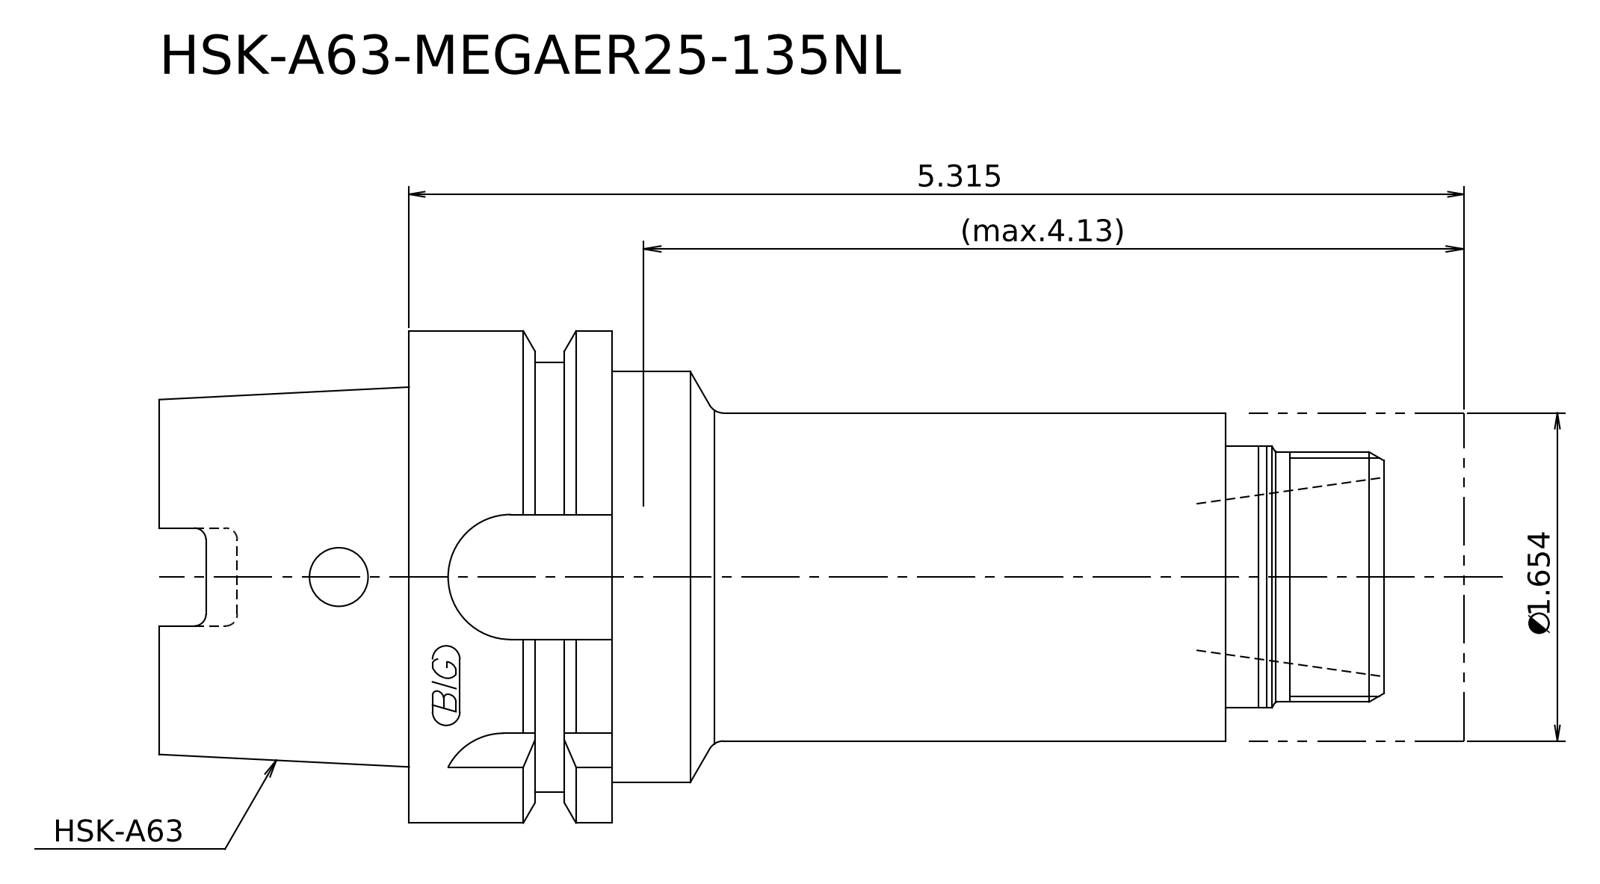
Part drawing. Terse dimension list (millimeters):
written by: Kubotek KeyCreator 2011 V10.0.2 (22737) (automotive_design)
unit: mm
bodies: 2 solids, 23 faces (9 planar, 8 cylindrical, 6 other)
size: 167 × 63 × 63
volume: 306 165 mm³; area: 35 521 mm²
bosses: 1× ⌀63, 1× ⌀55, 1× ⌀52.6, 1× ⌀42, 1× ⌀33.5, 1× ⌀32
face distances: 139.5, 27.5, 167, 135, 107.5, 32, 109, 81.5, 26, 58
